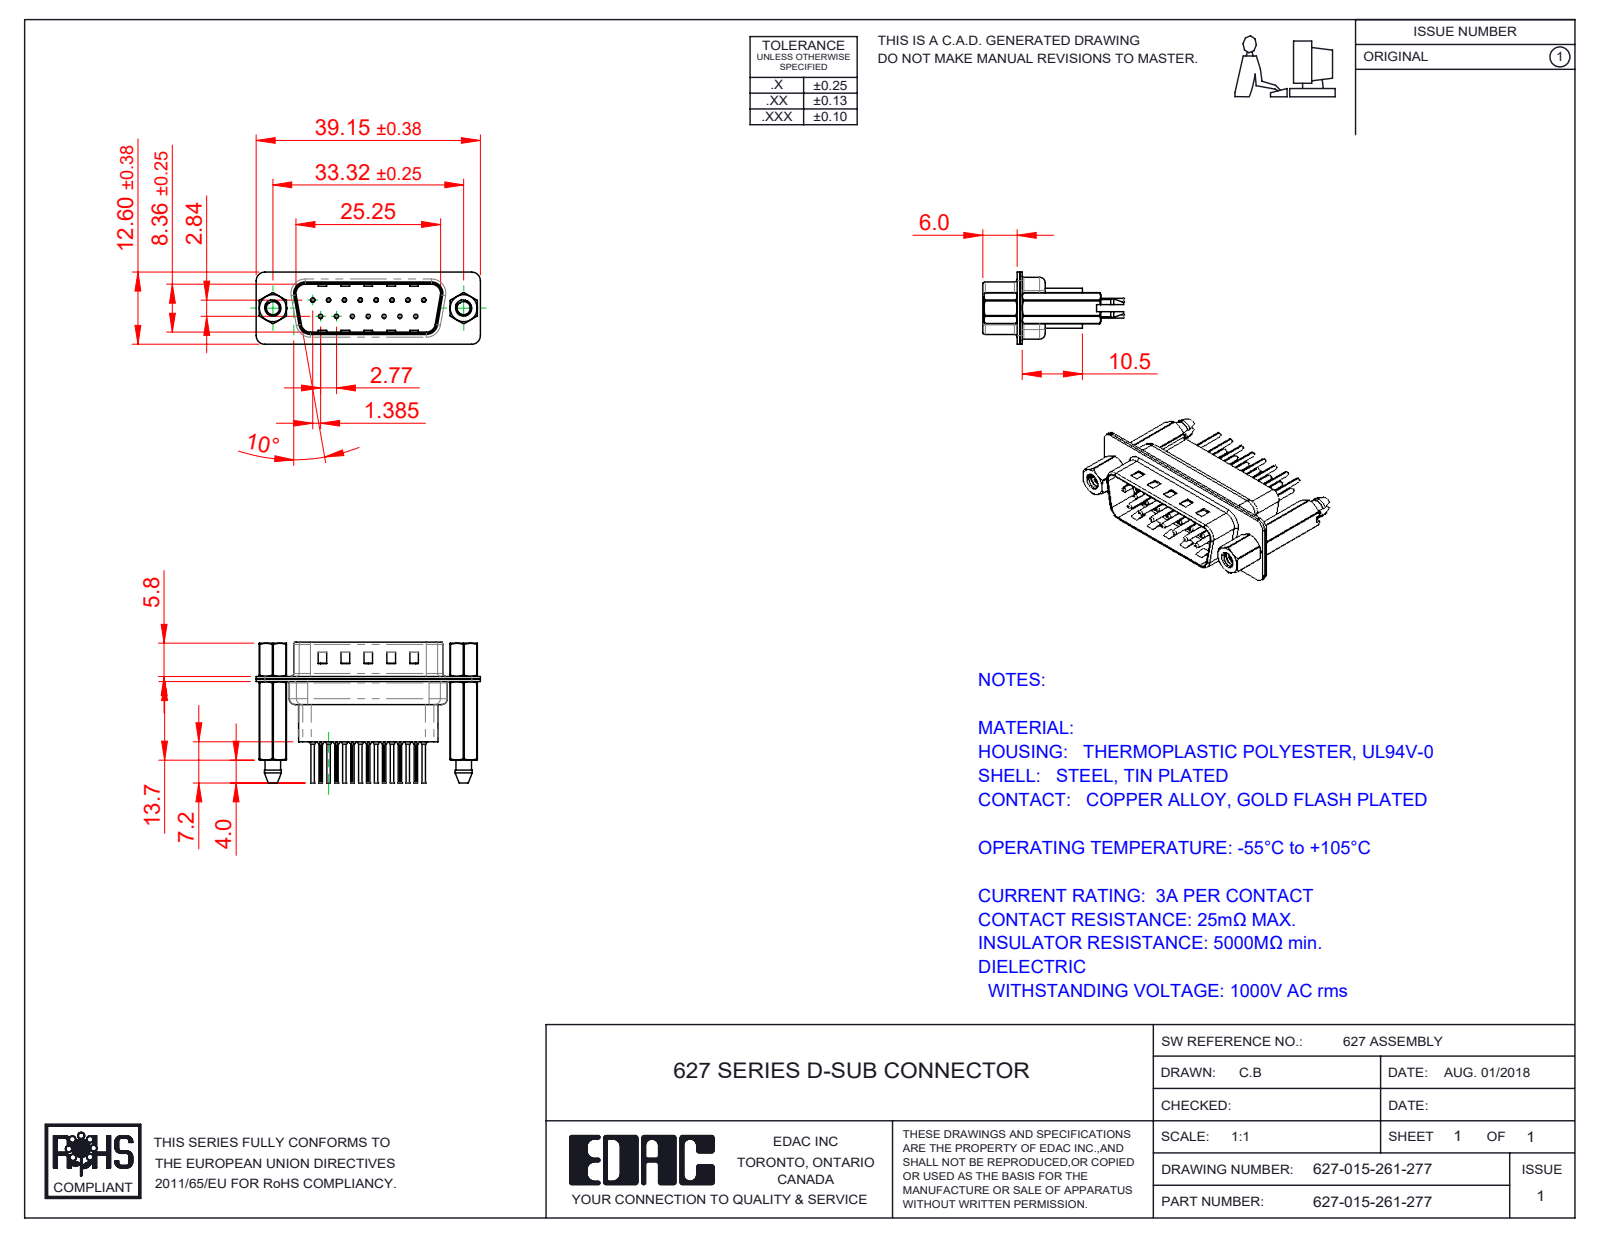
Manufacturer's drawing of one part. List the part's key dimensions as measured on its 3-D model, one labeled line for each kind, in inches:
Part name (STEP PRODUCT): 627 4-40 Threaded Boardlock_HP61; 627-015-261-077; 627 4-40 Hex Standoff; 627 Contact Row 2_61 (+4 more)
STEP written by: SolidWorks 2020 (CONFIG_CONTROL_DESIGN)
Units: inches
Bodies: 22 solids, 2044 faces (553 planar, 826 cylindrical, 665 other)
Overall size (bounding box): 1.541 × 0.969 × 0.496
Volume: 0.19 in³ · Surface area: 12.36 in²
Round holes (diameter × count): ⌀0.008 ×15, ⌀0.014 ×15, ⌀0.043 ×15, ⌀0.063 ×15, ⌀0.089 ×2, ⌀0.09 ×2, ⌀0.157 ×2, ⌀0.189 ×2
Round bosses / shafts (diameter × count): ⌀0.079 ×15, ⌀0.059 ×15, ⌀0.03 ×15, ⌀0.024 ×15, ⌀0.193 ×2, ⌀0.11 ×2
Partial cylindrical surfaces — rounded edges, fillets, slot ends (radius × count): R0.004 ×30, R0.059 ×18, R0.079 ×12, R0.063 ×10, R0.02 ×8, R0.01 ×4, R0.024 ×4, R0.026 ×4
Main face-to-face distances: 0.016, 0.018, 0.187, 0.035, 0.032, 0.377, 0.059, 0.027, 0.302, 0.656
Hole centre spacings: 0.124, 0.109, 0.218, 0.327, 0.436, 0.198, 0.198, 0.294
